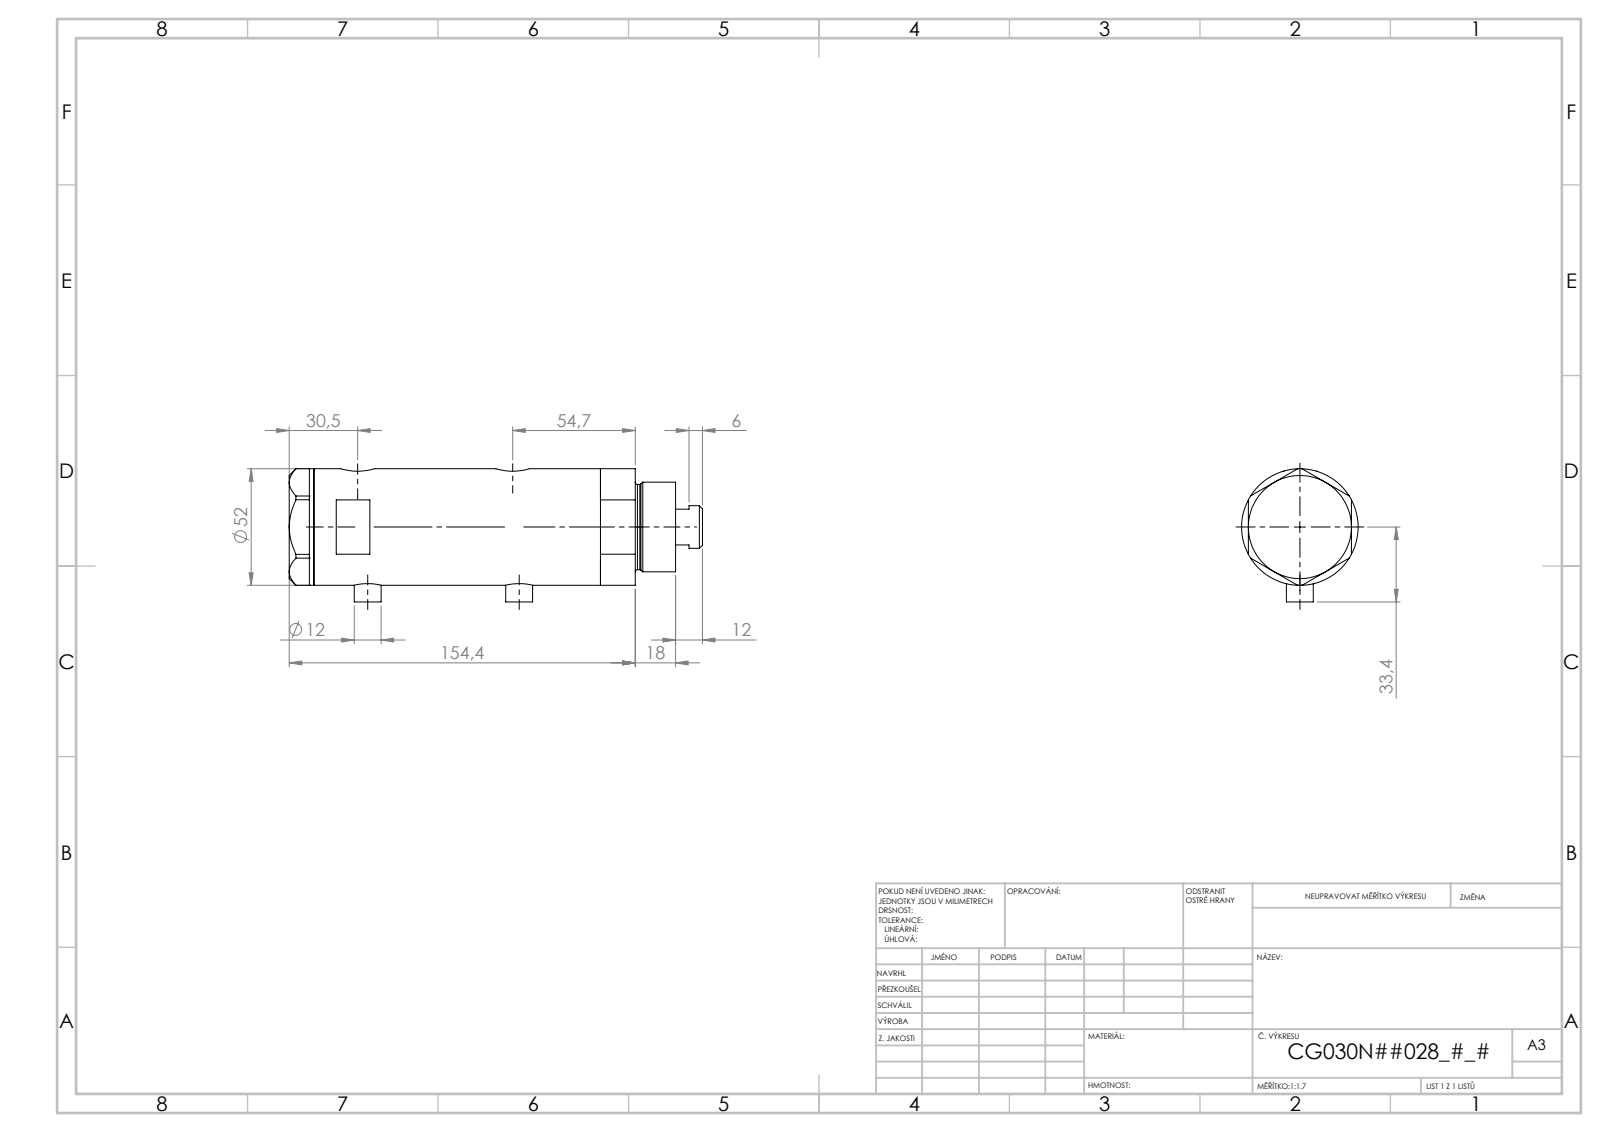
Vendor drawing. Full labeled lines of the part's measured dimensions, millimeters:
Part name (STEP PRODUCT): V270CG_FRONT; V270CG_VC; V270CG_MIDDLE; V270CG_BACK
STEP written by: SolidWorks 2019 (CONFIG_CONTROL_DESIGN)
Units: millimetres
Bodies: 4 solids, 140 faces (67 planar, 53 cylindrical, 20 other)
Overall size (bounding box): 177.02 × 53.1 × 52
Volume: 315 987 mm³ · Surface area: 74 062 mm²
Round holes (diameter × count): ⌀5 ×2, ⌀9.73 ×2, ⌀12.5 ×2, ⌀15 ×2, ⌀6.5 ×1, ⌀20 ×1, ⌀21.5 ×1, ⌀30 ×1, ⌀33 ×1, ⌀44 ×1
Round bosses / shafts (diameter × count): ⌀12 ×2, ⌀52 ×1, ⌀40 ×1, ⌀38 ×1, ⌀19 ×1
Main face-to-face distances: 23.81, 10.99, 34.8, 46, 92.55, 81.56, 57.75, 128.95, 117.96, 94.15
Hole centre spacings: 2.9, 4.5, 54.75, 57.65, 59.25, 62.15, 2.89, 2.91
